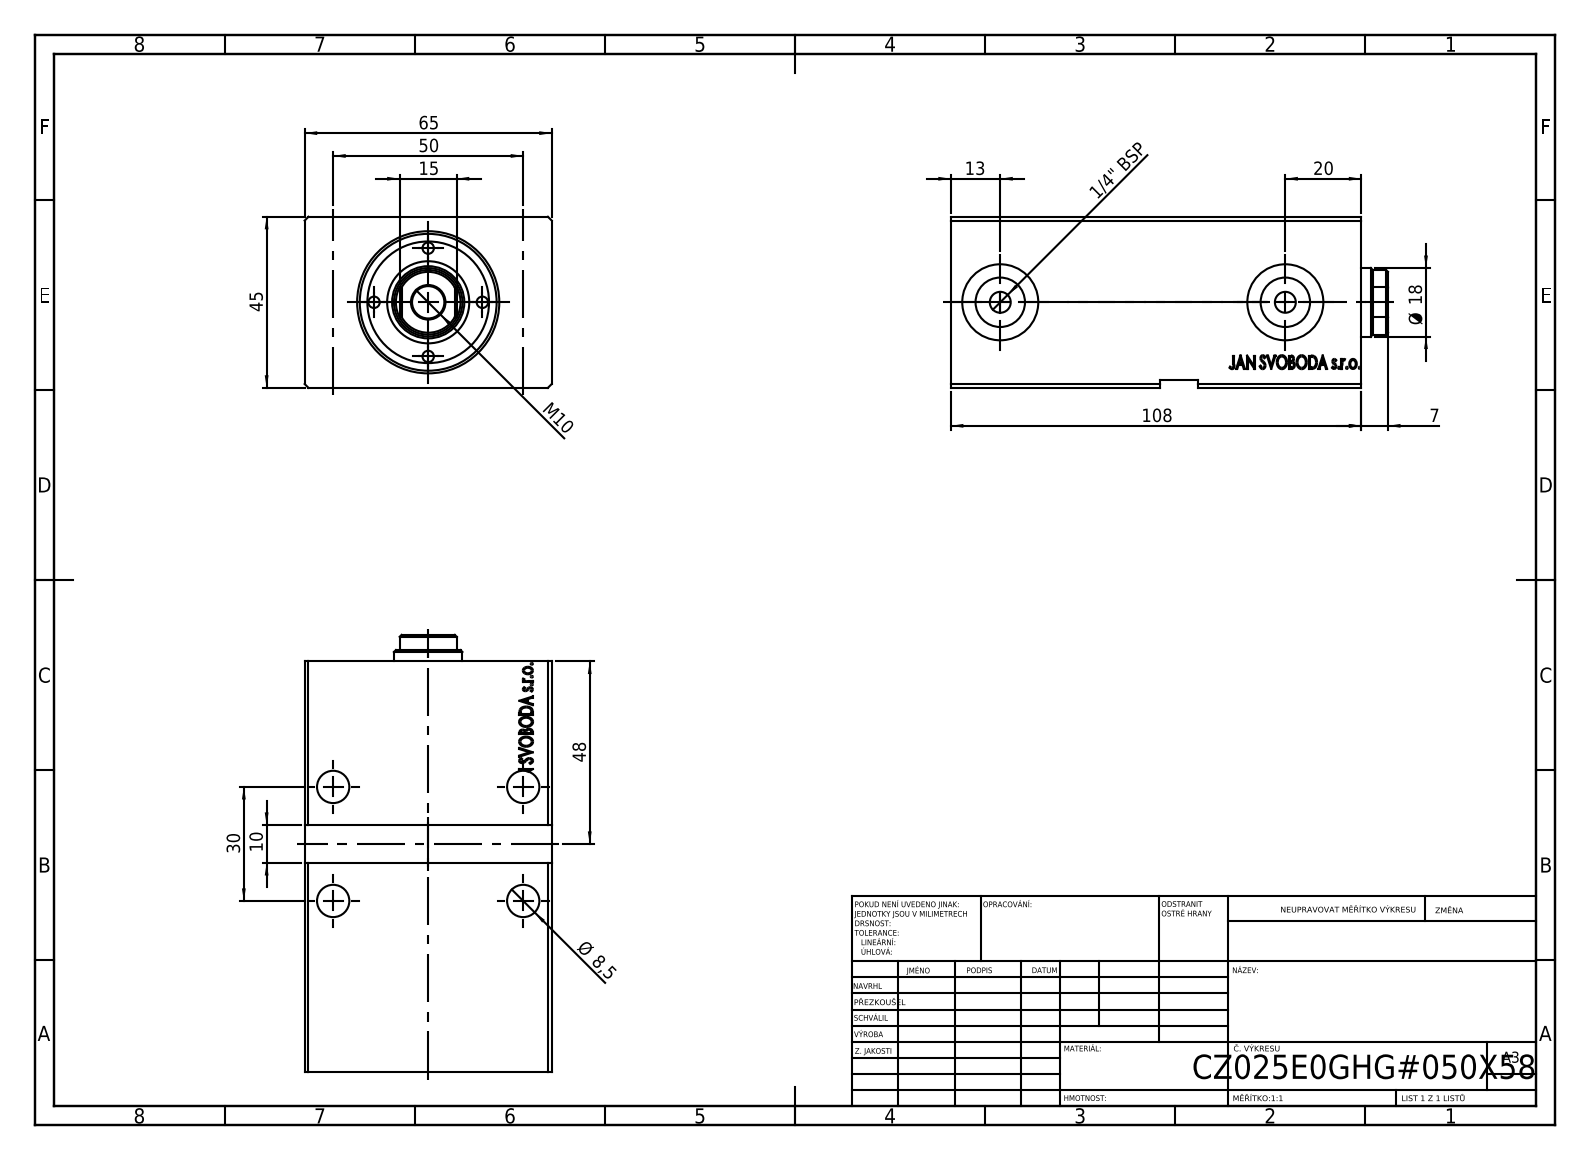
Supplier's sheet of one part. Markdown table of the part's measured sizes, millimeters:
| quantity | value |
| --- | --- |
| STEP written by | SolidWorks 2019 (CONFIG_CONTROL_DESIGN) |
| units | millimeters |
| bodies | 1 solid, 752 faces (350 planar, 30 cylindrical, 372 other) |
| overall size | 108 × 65 × 45 |
| volume | 249 495 mm³ |
| surface area | 43 055 mm² |
| round holes (diameter × count) | 8.5 × 4, 5.5 × 2, 8 × 2, 13 × 2, 20 × 2, 25 × 1, 36 × 1 |
| main face-to-face distances | 45, 65, 108, 107.8, 43, 2, 7, 100.8, 101, 95.2 |
| hole center spacings | 30, 50, 58.31, 16.28, 27.2, 34.13, 36.67, 40.5 |
